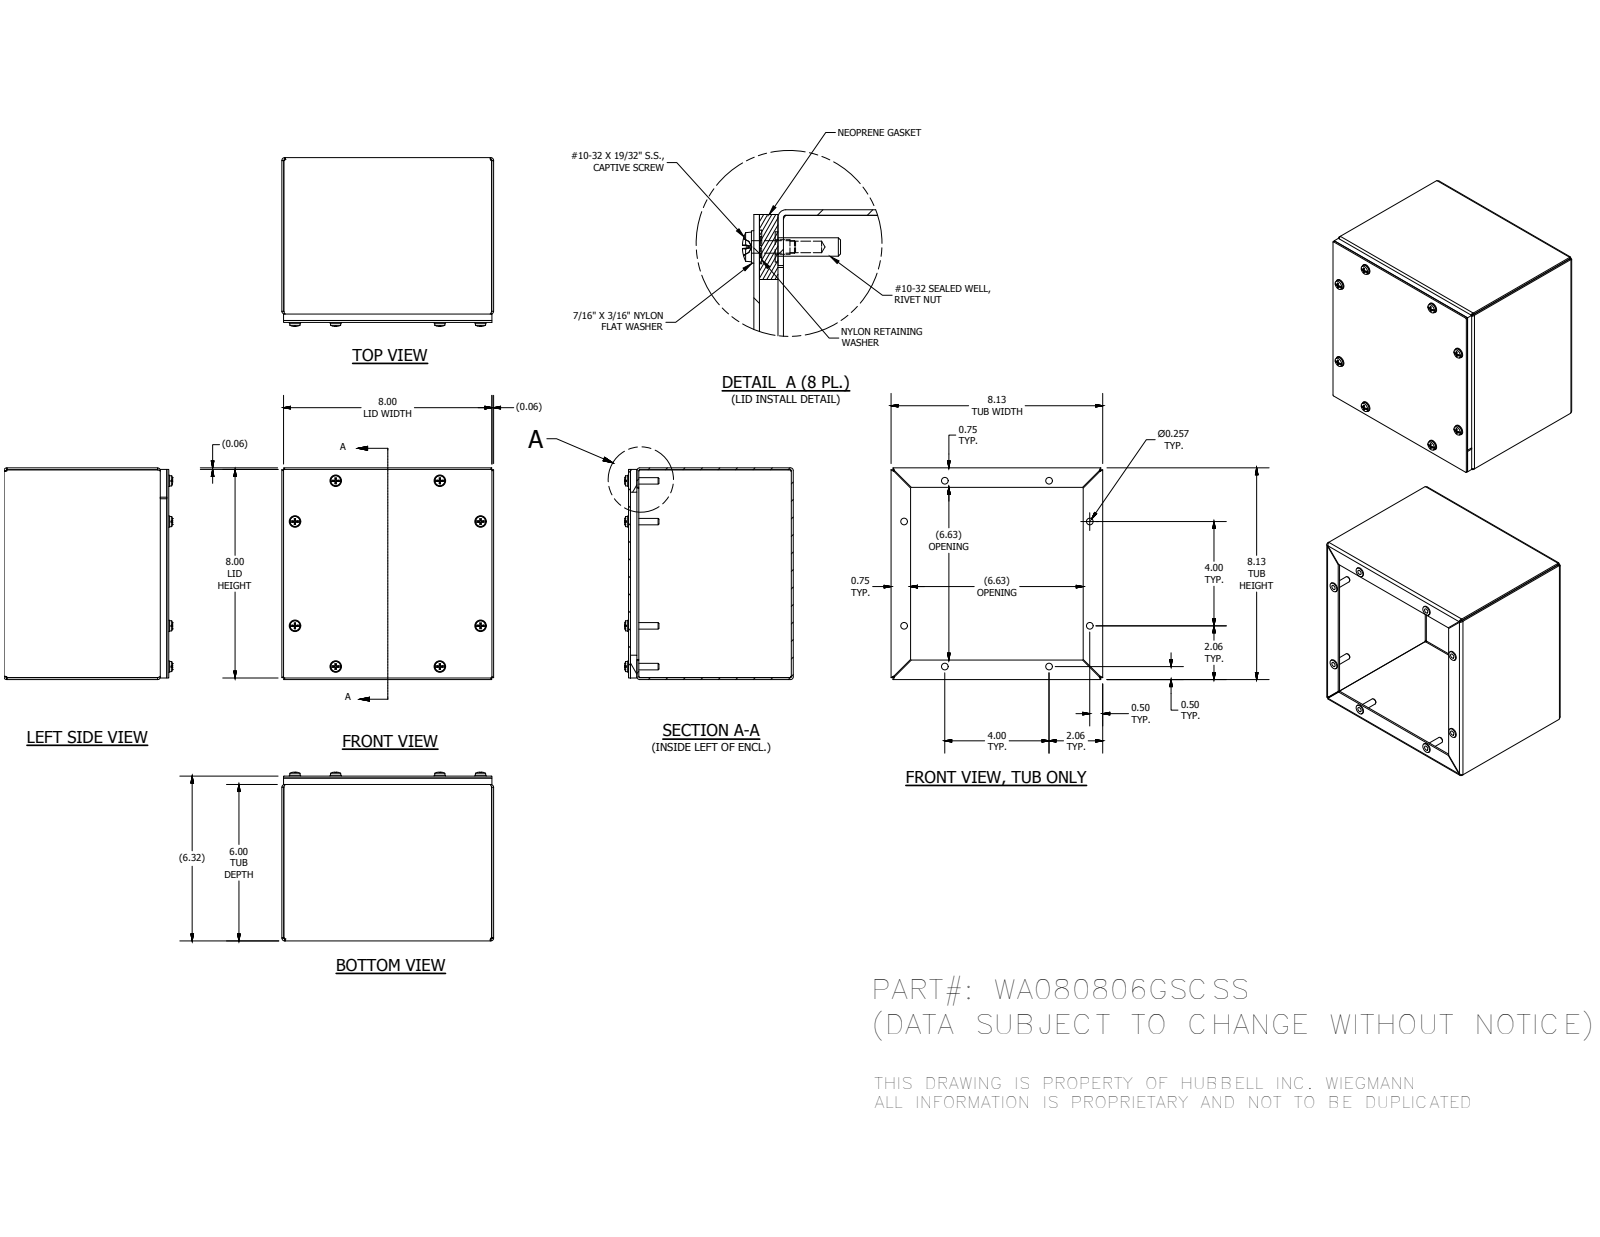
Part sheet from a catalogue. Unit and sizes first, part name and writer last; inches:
Units: inches
Overall size (bounding box): 8.125 × 8.125 × 6.479
Round holes (diameter × count): ⌀0.156 ×8, ⌀0.188 ×8, ⌀0.196 ×8, ⌀0.257 ×8, ⌀0.278 ×8, ⌀0.281 ×8, ⌀0.313 ×8
Round bosses / shafts (diameter × count): ⌀0.453 ×8, ⌀0.437 ×8, ⌀0.406 ×8, ⌀0.248 ×8, ⌀0.167 ×8
Partial cylindrical surfaces — rounded edges, fillets, slot ends (radius × count): R0.031 ×12, R0.07 ×8, R0.089 ×8, R0.105 ×8
Main face-to-face distances: 0.074, 8.051, 6.25, 8.125, 7.977, 6.324, 6.176, 5.926, 0.324, 0.25
Hole centre spacings: 4, 2.209, 5.777, 5.777, 5.778, 5.778, 7.124, 7.866
Volume: 31.46 in³ · Surface area: 768.5 in²
Bodies: 36 solids, 764 faces (420 planar, 160 cylindrical, 184 other)
Part name (STEP PRODUCT): WA080806GSCSSBKP; WA0808GSCSSLID; 316280; 37210 (+4 more)
STEP written by: Autodesk Inventor 2016 (AUTOMOTIVE_DESIGN)
